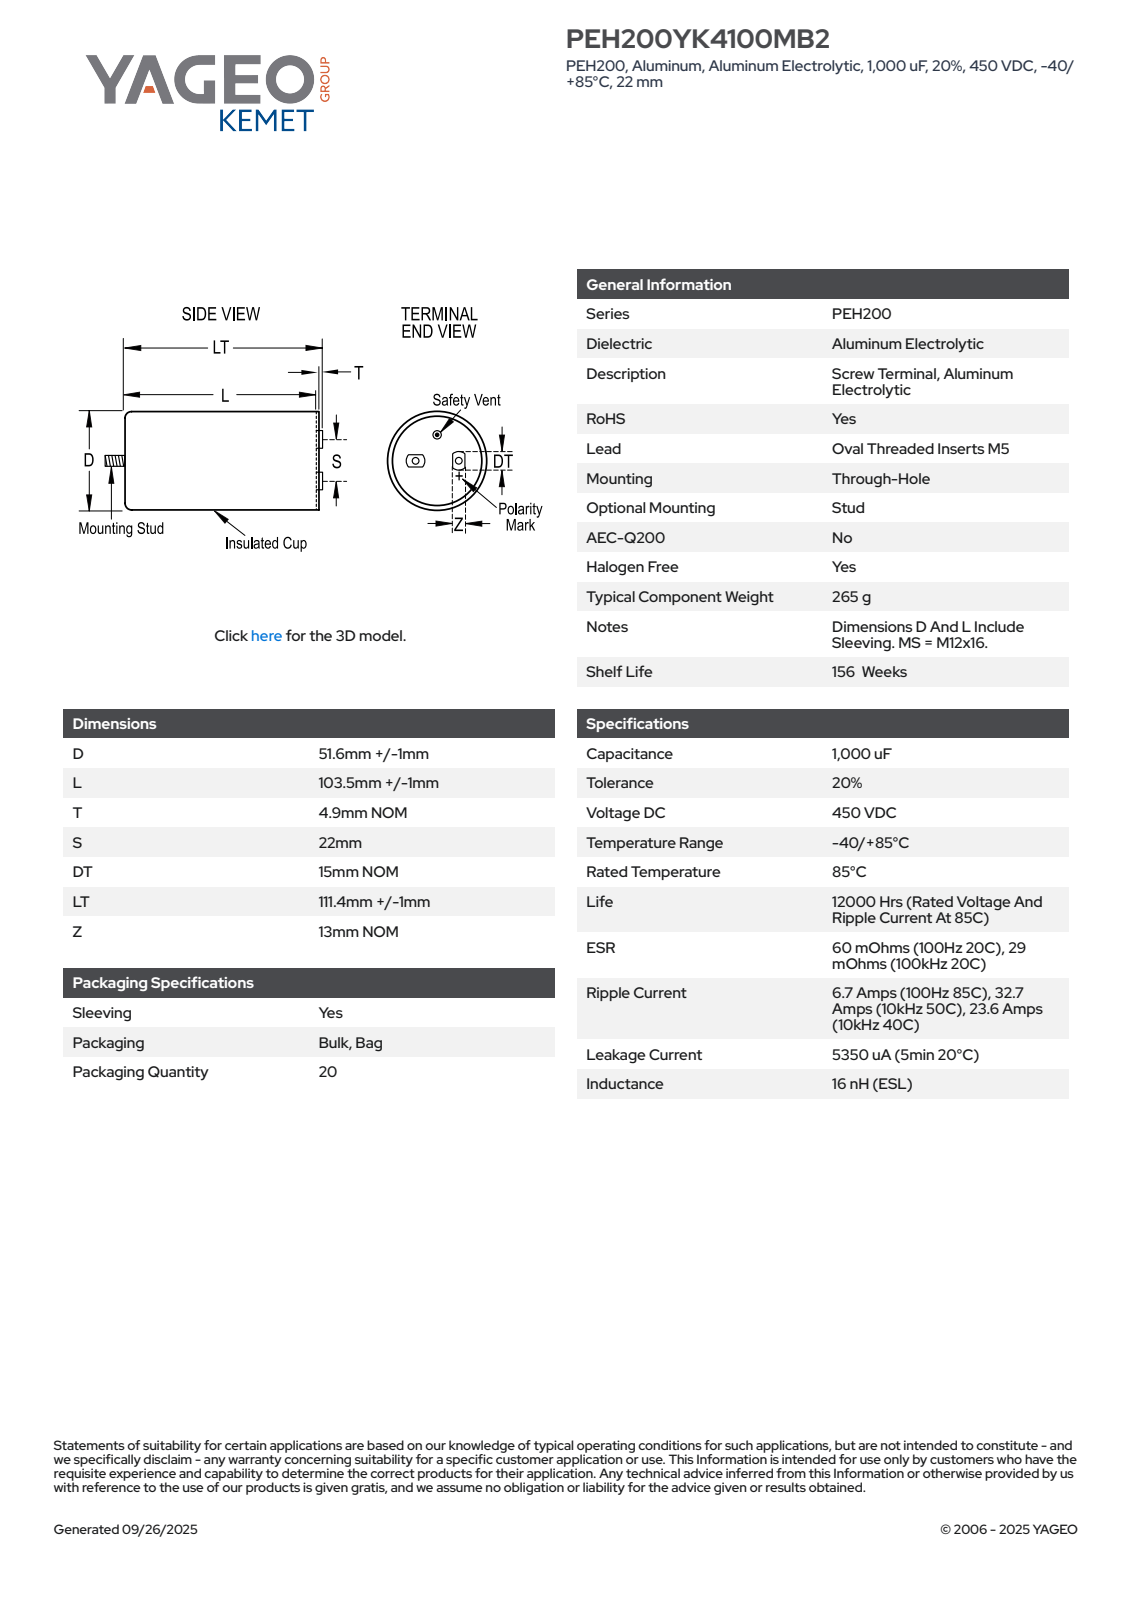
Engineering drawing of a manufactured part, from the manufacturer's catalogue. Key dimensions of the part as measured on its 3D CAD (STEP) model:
Part name (STEP PRODUCT): CARCS_D52.6L104.5S22T4.9; Stud; Oval_Terminal_18; Can_18
STEP written by: SolidWorks 2014 (AUTOMOTIVE_DESIGN)
Units: millimetres
Bodies: 4 solids, 185 faces (70 planar, 83 cylindrical, 32 other)
Overall size (bounding box): 128.4 × 52.6 × 52.6
Volume: 231 647 mm³ · Surface area: 25 210 mm²
Round holes (diameter × count): ⌀4.02 ×2, ⌀50.6 ×1
Round bosses / shafts (diameter × count): ⌀7.5 ×2, ⌀52.6 ×1, ⌀12 ×1, ⌀11.6 ×1
Partial cylindrical surfaces — rounded edges, fillets, slot ends (radius × count): R7.5 ×2, R26.29 ×1
Main face-to-face distances: 104.5, 7.9, 112.4, 3, 107.5, 4.9, 13, 5, 128.4, 123.5
Hole centre spacings: 11, 22
